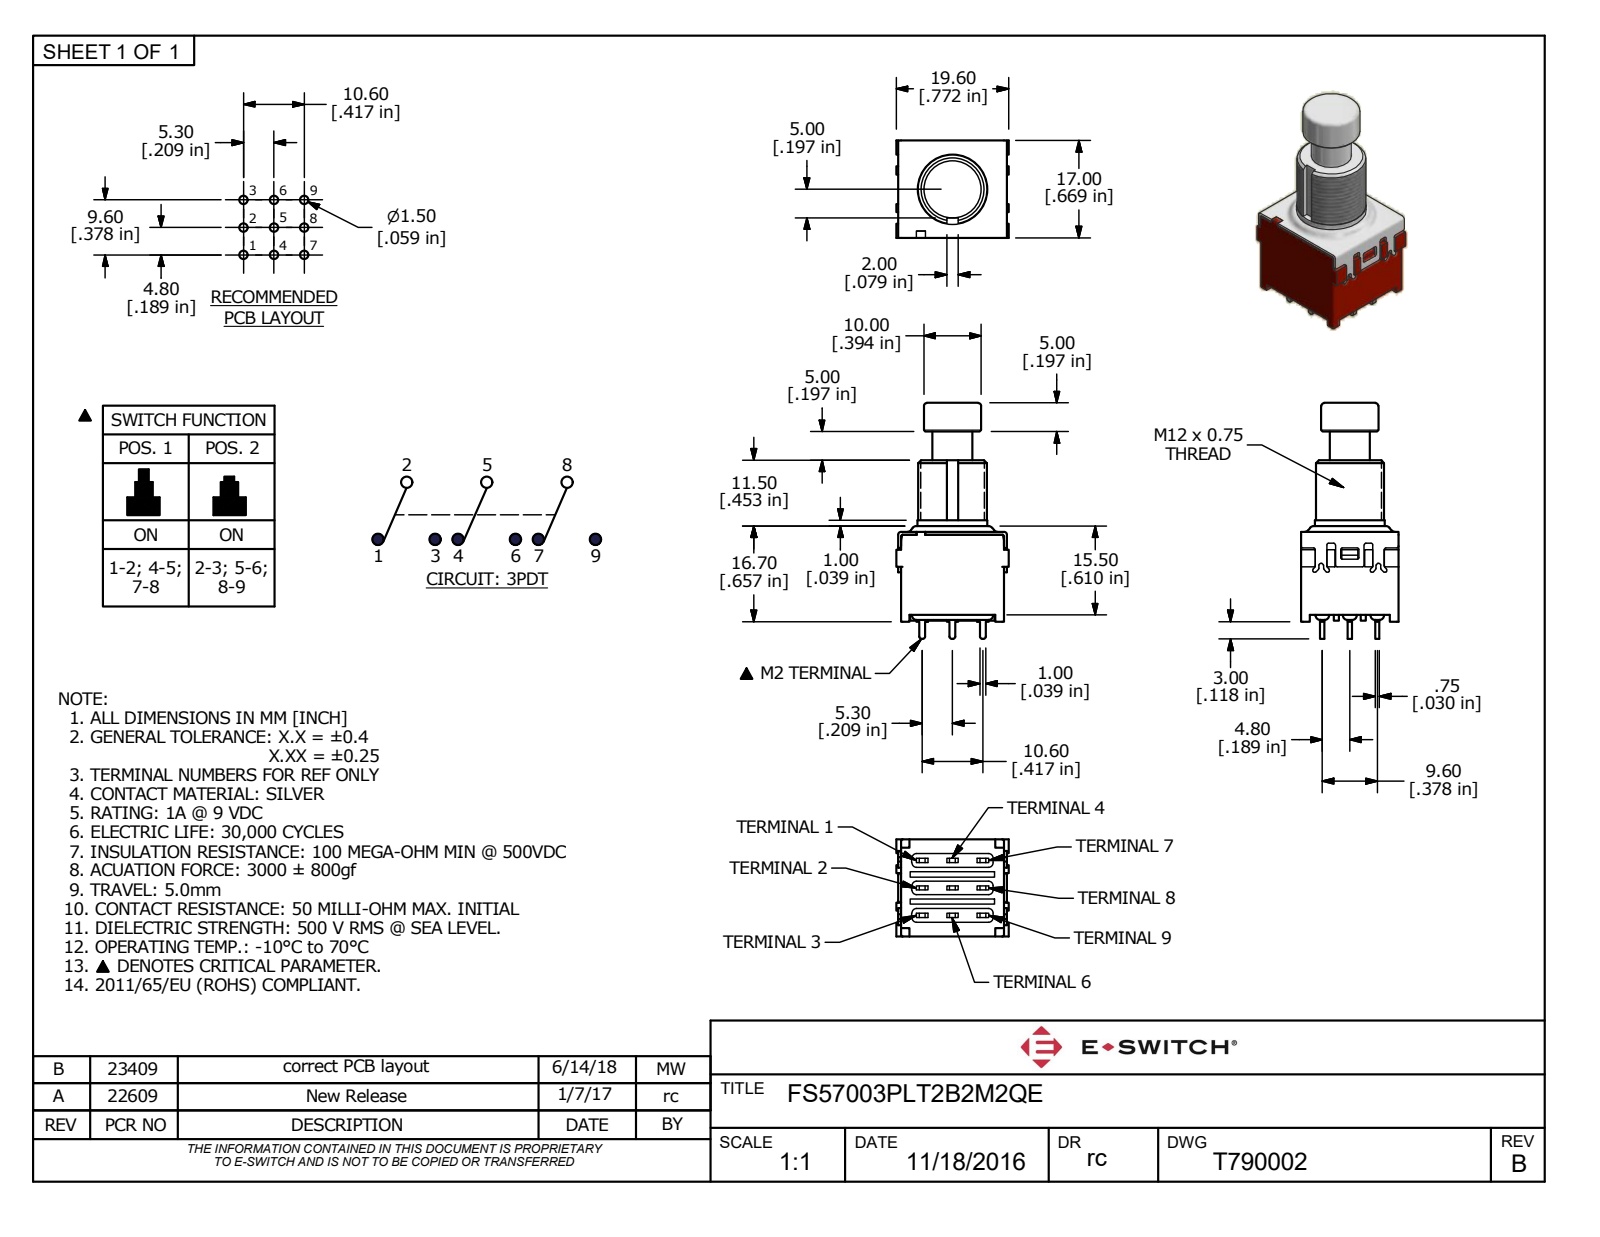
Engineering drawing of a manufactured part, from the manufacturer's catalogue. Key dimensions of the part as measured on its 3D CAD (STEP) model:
Part name (STEP PRODUCT): T790002; FS5700 3P Housing; FS5700 3P Top Plate; FS5700 3P M2 Terminal (+3 more)
STEP written by: Autodesk Inventor 2012 (AUTOMOTIVE_DESIGN)
Units: millimetres
Bodies: 8 solids, 428 faces (276 planar, 128 cylindrical, 24 other)
Overall size (bounding box): 41.2 × 19.6 × 17
Volume: 3 127 mm³ · Surface area: 5 728 mm²
Round holes (diameter × count): ⌀7 ×1, ⌀9 ×1, ⌀11 ×1
Round bosses / shafts (diameter × count): ⌀12.2 ×1, ⌀12 ×1, ⌀11.6 ×1, ⌀10 ×1
Partial cylindrical surfaces — rounded edges, fillets, slot ends (radius × count): R0.3 ×36, R0.8 ×20, R0.4 ×6, R0.5 ×6
Main face-to-face distances: 1.2, 15.8, 16.8, 17, 0.5, 18, 1, 14.6, 15.6, 10
